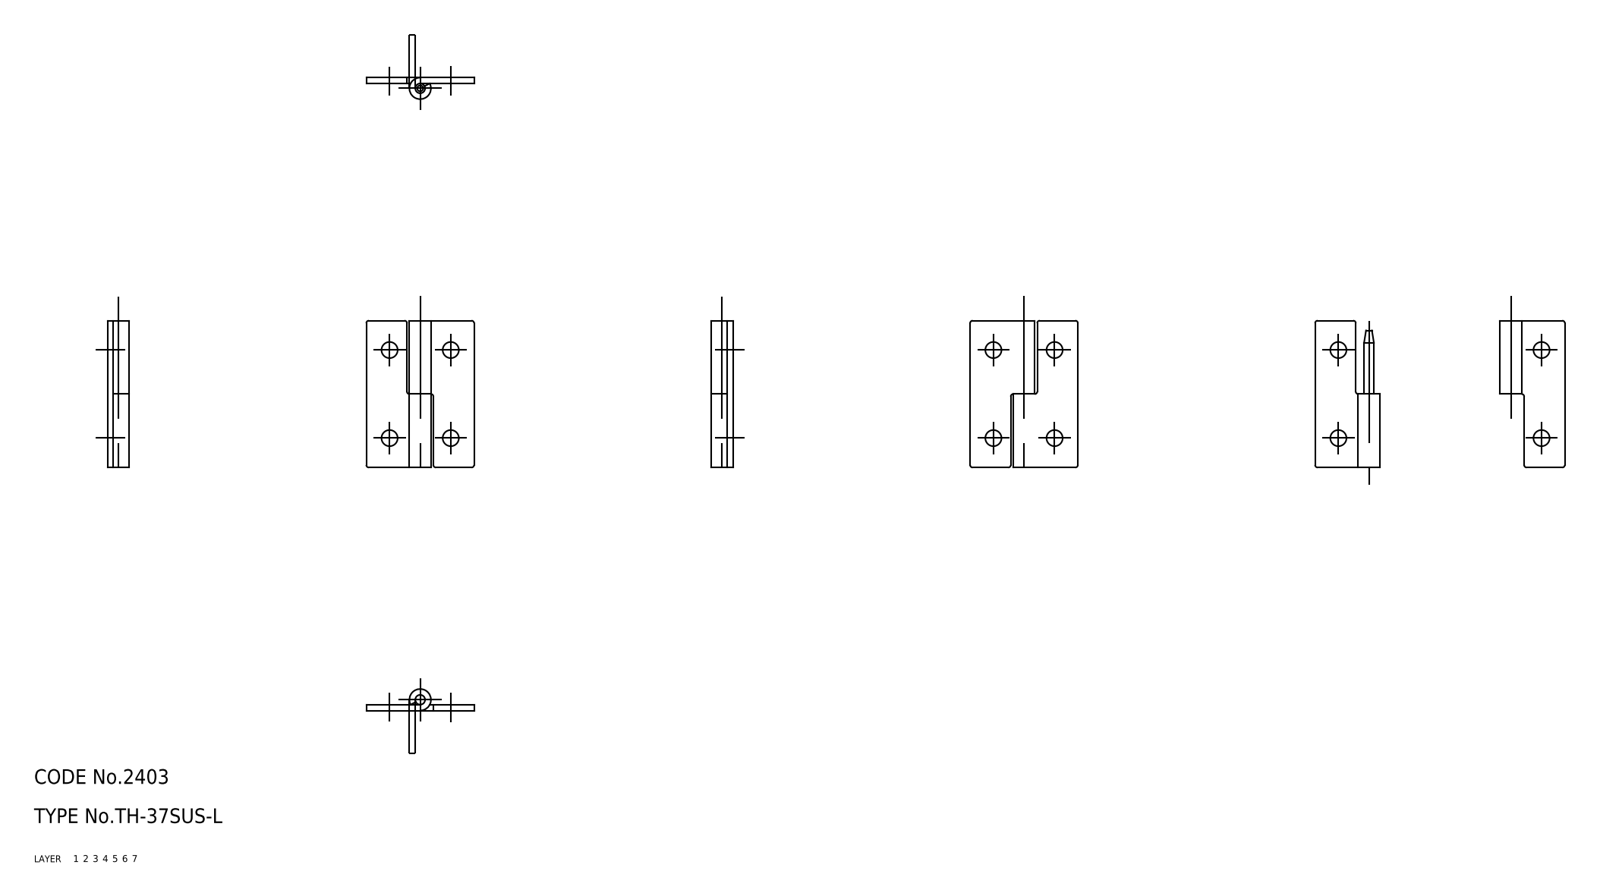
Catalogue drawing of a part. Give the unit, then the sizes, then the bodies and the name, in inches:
Units: inches
Overall size (bounding box): 1.181 × 0.866 × 0.173
Volume: 0.063 in³ · Surface area: 3.171 in²
Bodies: 3 solids, 42 faces (0 planar, 0 cylindrical, 42 other)
Part name (STEP PRODUCT): shaft; hinge piece_B; hinge piece_A; TH_37SUS_L_8448_36
STEP written by: CADfix (AUTOMOTIVE_DESIGN)
